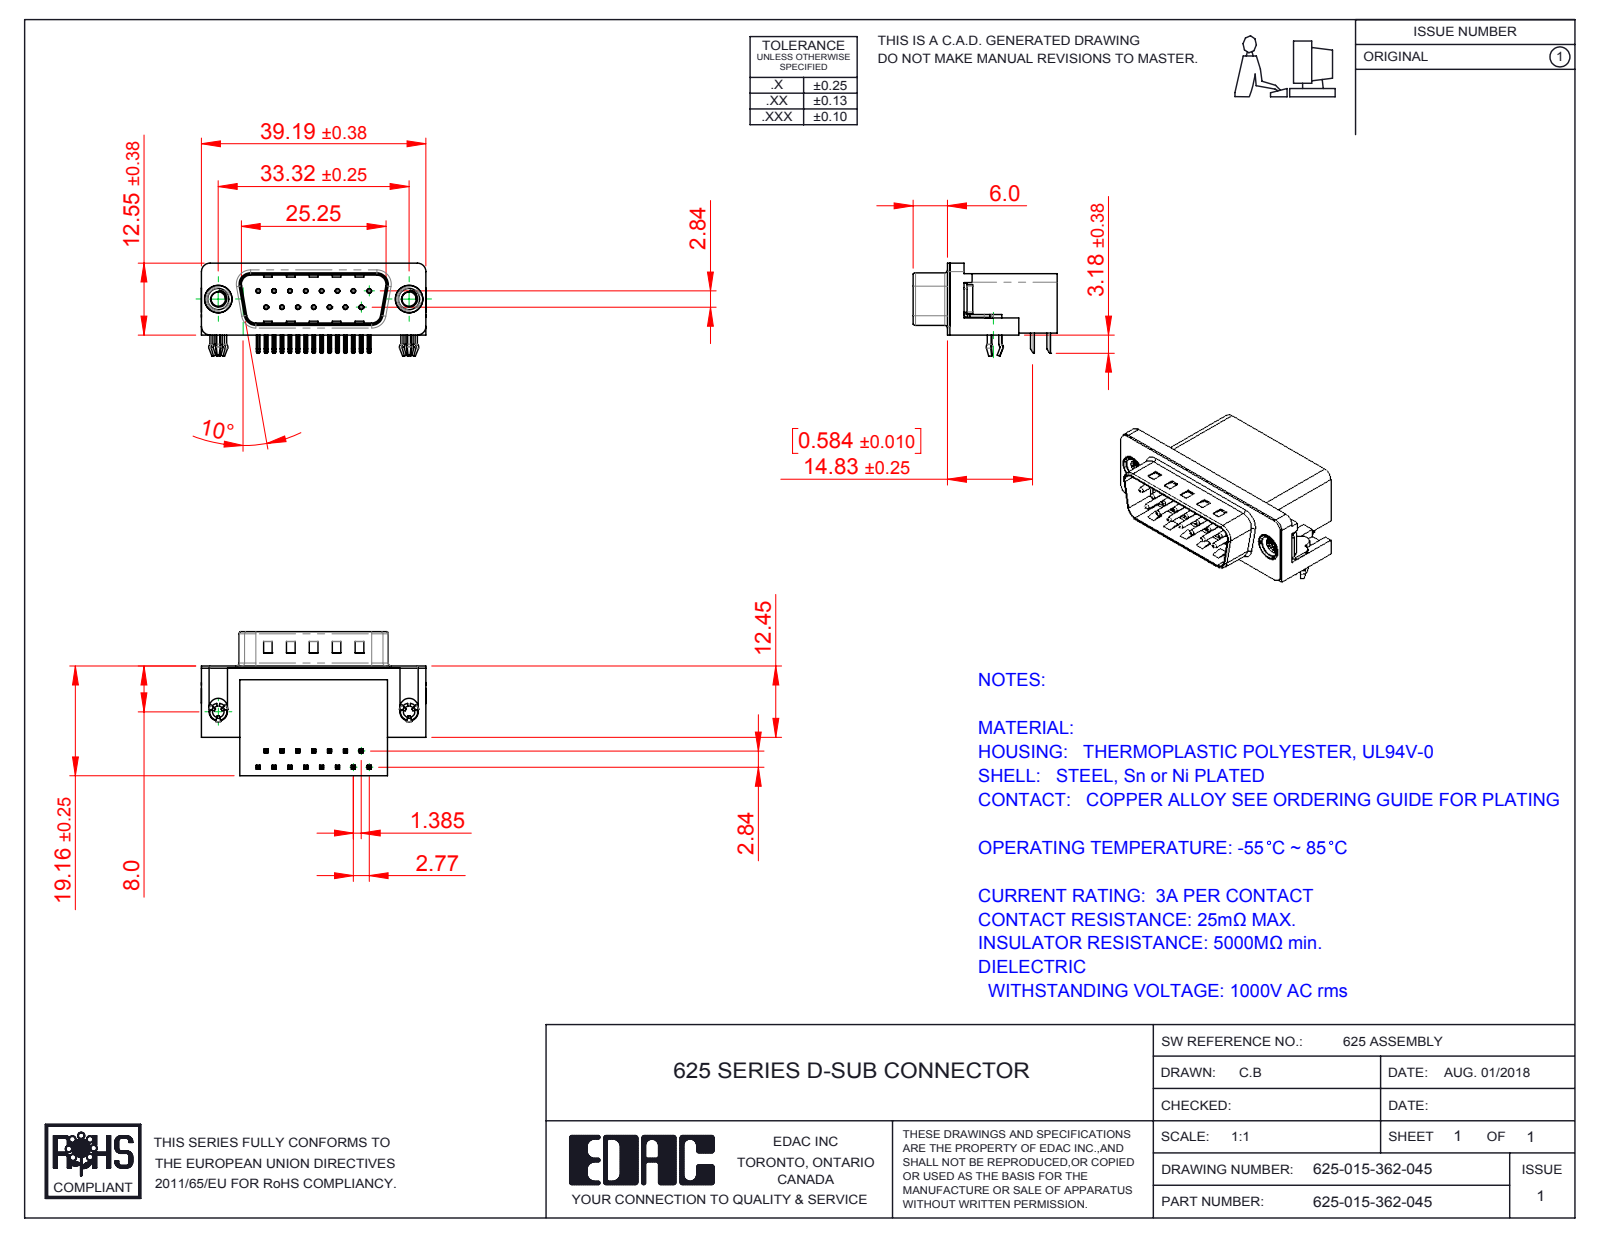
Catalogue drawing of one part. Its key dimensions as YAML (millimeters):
part_name: "625 3 Prong Board Lock; 625 Contact Top; 625 Contact Bottom; 625 Housing_15 Socket (+3 more)"
step_written_by: "SolidWorks 2016 (CONFIG_CONTROL_DESIGN)"
units: millimeters
bodies: {solids: 21, faces: 1583, planar: 931, cylindrical: 457, other: 195}
overall_size: [39.22, 25.16, 16.25]
volume: 6246
surface_area: 6489
round_holes:
  - {diameter: 0.35, count: 15}
  - {diameter: 0.8, count: 15}
  - {diameter: 2, count: 2}
  - {diameter: 2.5, count: 2}
  - {diameter: 4, count: 2}
  - {diameter: 4.8, count: 2}
  - {diameter: 5, count: 2}
round_bosses_or_shafts:
  - {diameter: 0.75, count: 15}
  - {diameter: 4.9, count: 2}
  - {diameter: 4.75, count: 2}
  - {diameter: 3.9, count: 2}
  - {diameter: 3, count: 2}
partial_cylinders:
  - {radius: 0.25, count: 72}
  - {radius: 0.12, count: 30}
  - {radius: 1, count: 16}
  - {radius: 0.5, count: 9}
  - {radius: 1.6, count: 8}
  - {radius: 1.5, count: 6}
  - {radius: 0.9, count: 4}
  - {radius: 2, count: 4}
face_to_face_distances: [0.4, 10.35, 18.76, 2.1, 10.46, 19.16, 1.7, 10.86, 8.76, 16.26]
hole_center_spacings: [3.16, 2.77, 5.54, 8.31, 11.08, 5.03, 5.04, 7.48]
